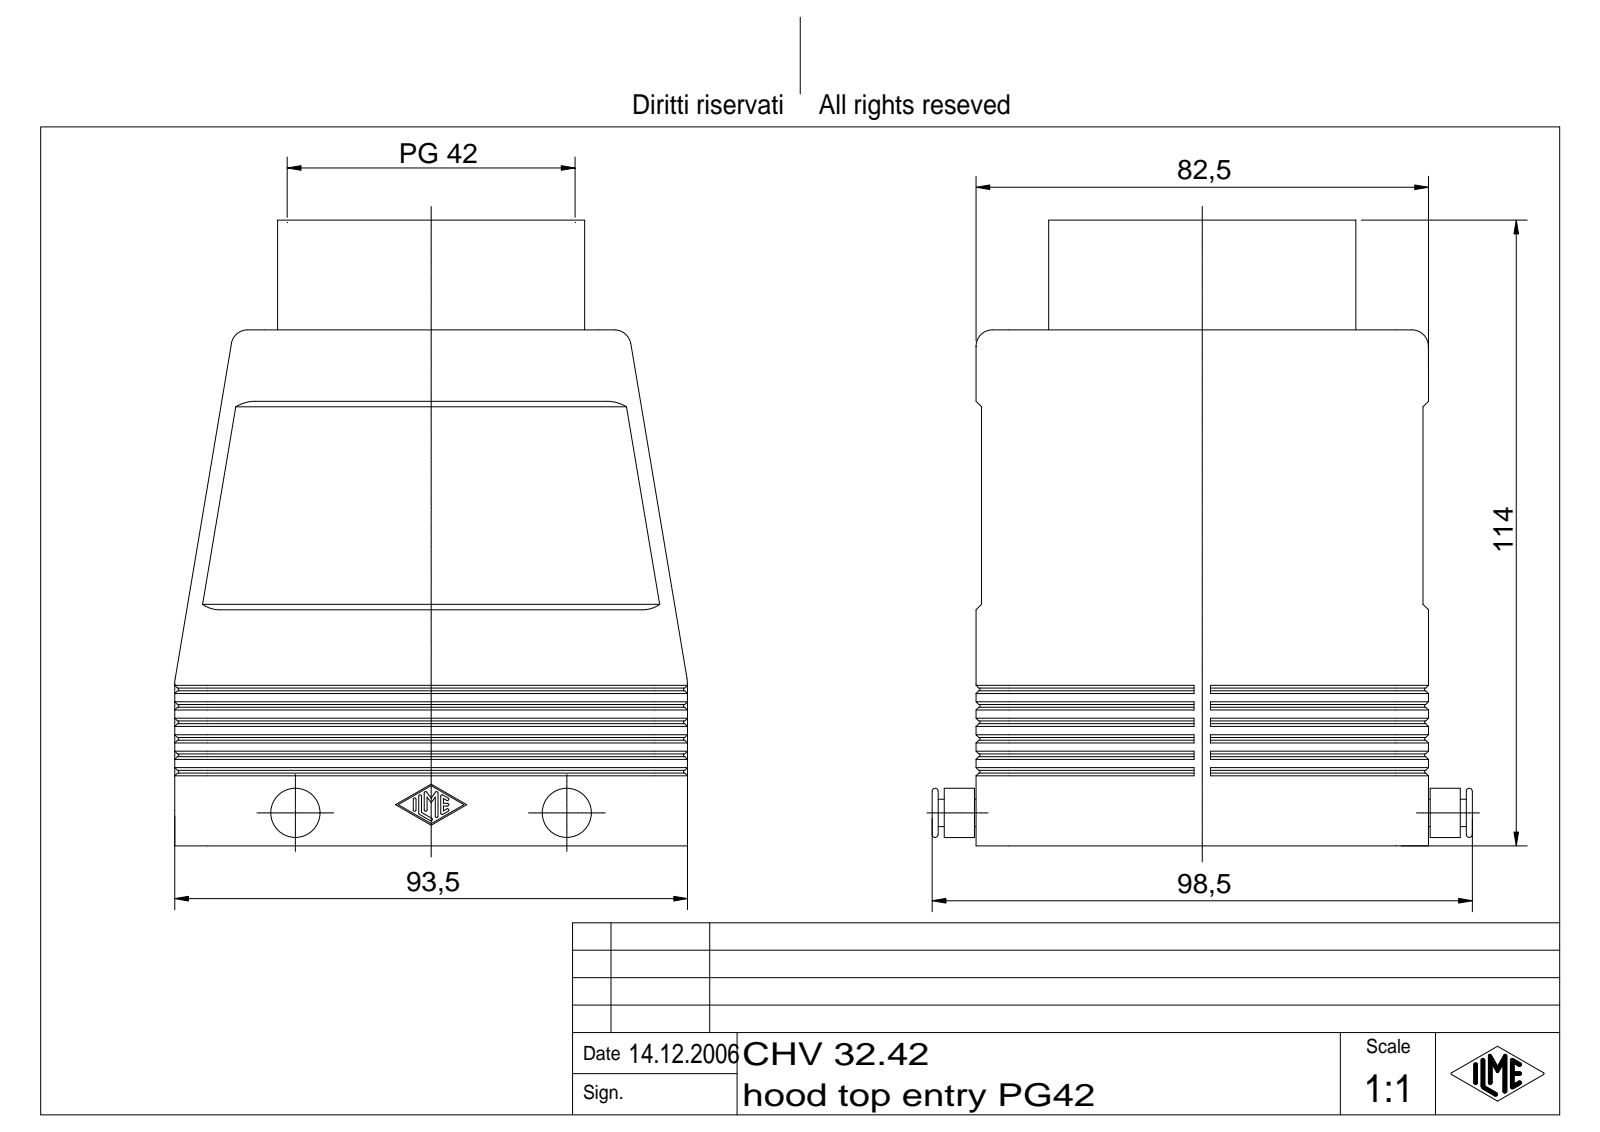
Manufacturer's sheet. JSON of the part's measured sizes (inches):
{"part_name": "CHV 32.42", "step_written_by": "Autodesk Inventor 7 (AUTOMOTIVE_DESIGN)", "units": "inches", "bodies": {"solids": 1, "faces": 617, "planar": 209, "cylindrical": 160, "other": 248}, "overall_size": [4.488, 3.878, 3.681], "volume_in3": 9.215, "surface_area_in2": 125, "round_holes": [[0.097, 4], [0.138, 4], [1.987, 1], [2.066, 1]], "round_bosses_or_shafts": [[0.354, 2], [0.197, 2], [2.559, 1], [2.205, 1]], "partial_cylinders_radius": [[0.01, 14], [0.079, 12], [0.236, 10], [0.118, 4], [0.209, 2]], "face_to_face_distances": [0.157, 3.091, 2.933, 3.248, 0.118, 0.039, 2.815, 0.433, 3.051, 3.209], "hole_center_spacings": [1.063, 1.534, 1.954, 3.051, 3.231]}
